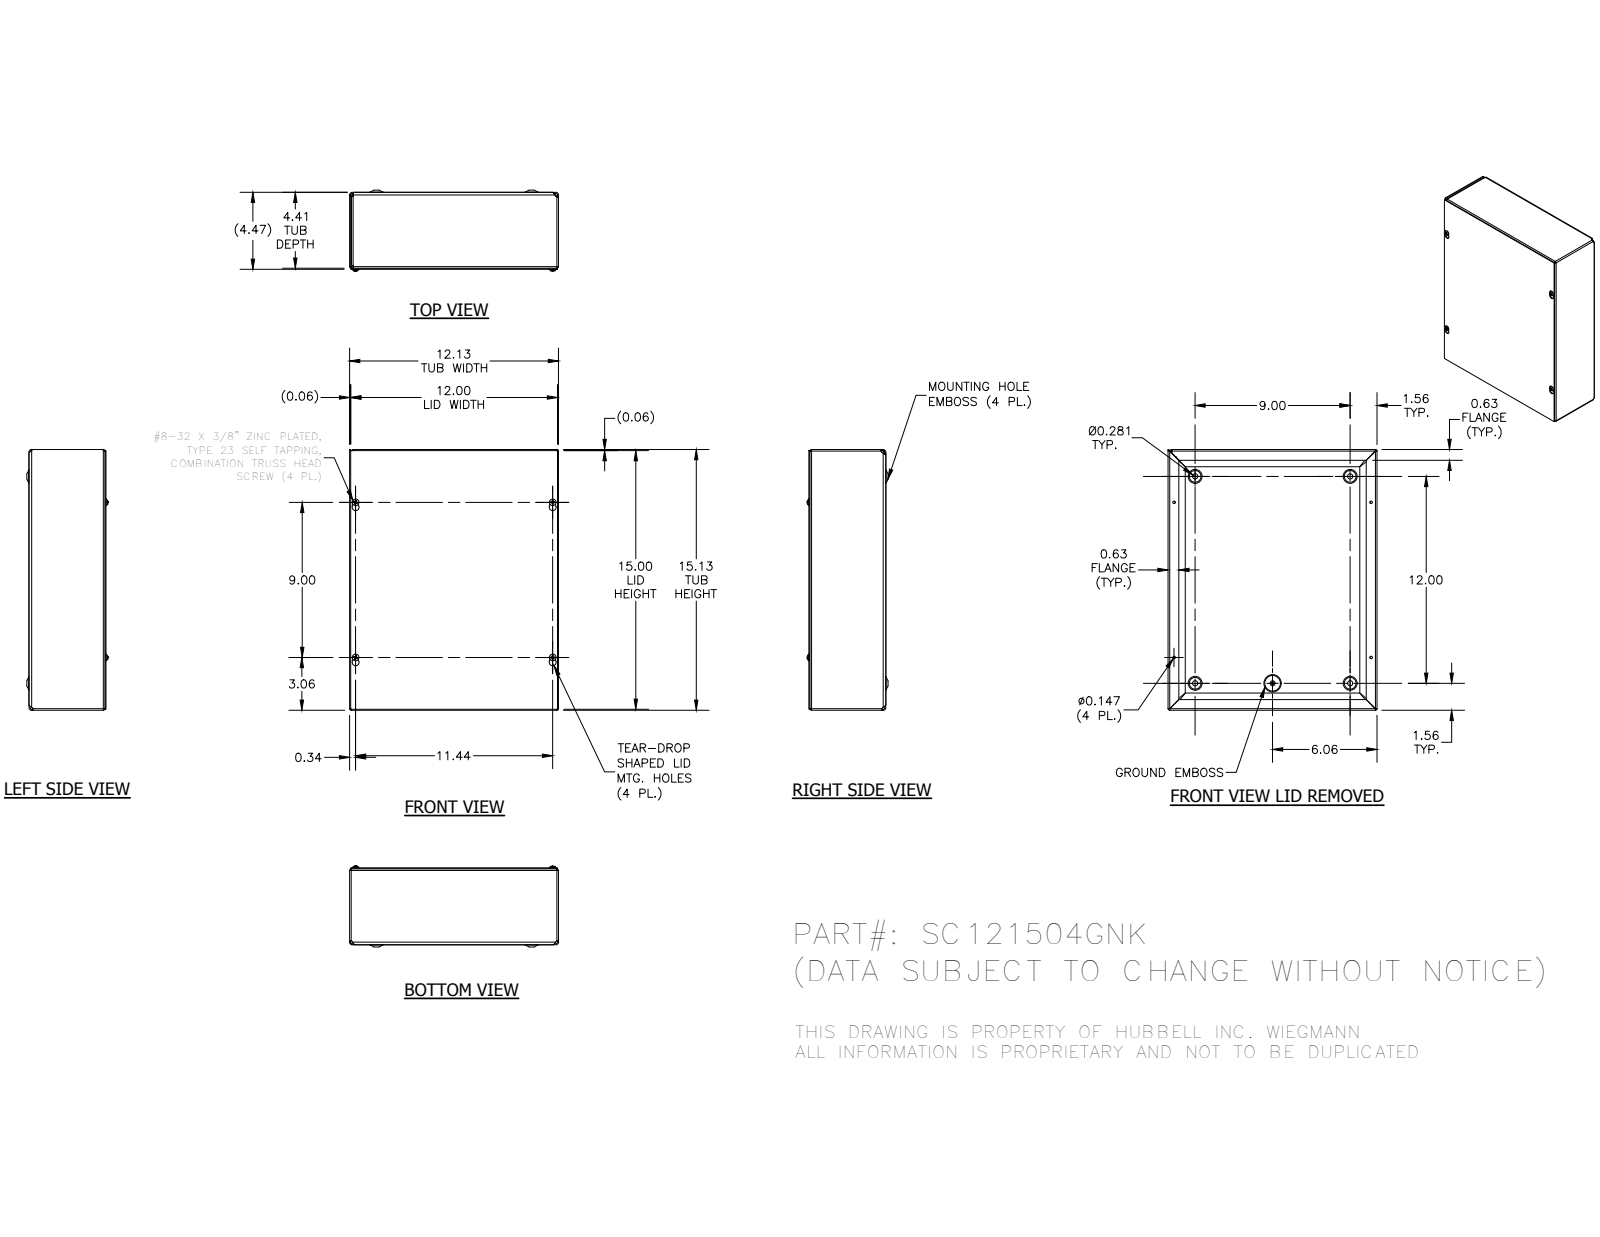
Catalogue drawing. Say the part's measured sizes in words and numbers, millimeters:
The part is named "SC1215GNKBKP; SC121504GNKWRA; SC1215GNKLID; 34056 (+1 more)". Its 3-D file was written by "Autodesk Inventor 2014 (AUTOMOTIVE_DESIGN)". It is 7 solids with 358 faces: 133 planar, 73 cylindrical and 152 other. Overall it measures 384.18 by 307.98 by 119.2 millimeters. Its volume is 675 459 cubic millimeters and its surface area 866 334 square millimeters. Round holes: 4 of diameter 3.73, 4 of diameter 7.62, 1 of diameter 4.19. Round bosses or shafts: 4 of diameter 9.75, 4 of diameter 4.17, 1 of diameter 5.8. Partial cylindrical surfaces (rounded edges, fillets, slot ends): 8 of radius 0.79, 8 of radius 2.37, 4 of radius 1.4, 4 of radius 1.57, 4 of radius 2.38, 4 of radius 2.97, 4 of radius 3.15, 4 of radius 3.17. The main face-to-face distances are 1.57, 110.32, 111.89, 1.59, 111.91, 113.48, 382.6, 1.58, 307.98, 306.41. The hole center spacings are 228.6, 114.3, 262.33, 262.34, 268.47, 268.51, 290.51, 304.8.
